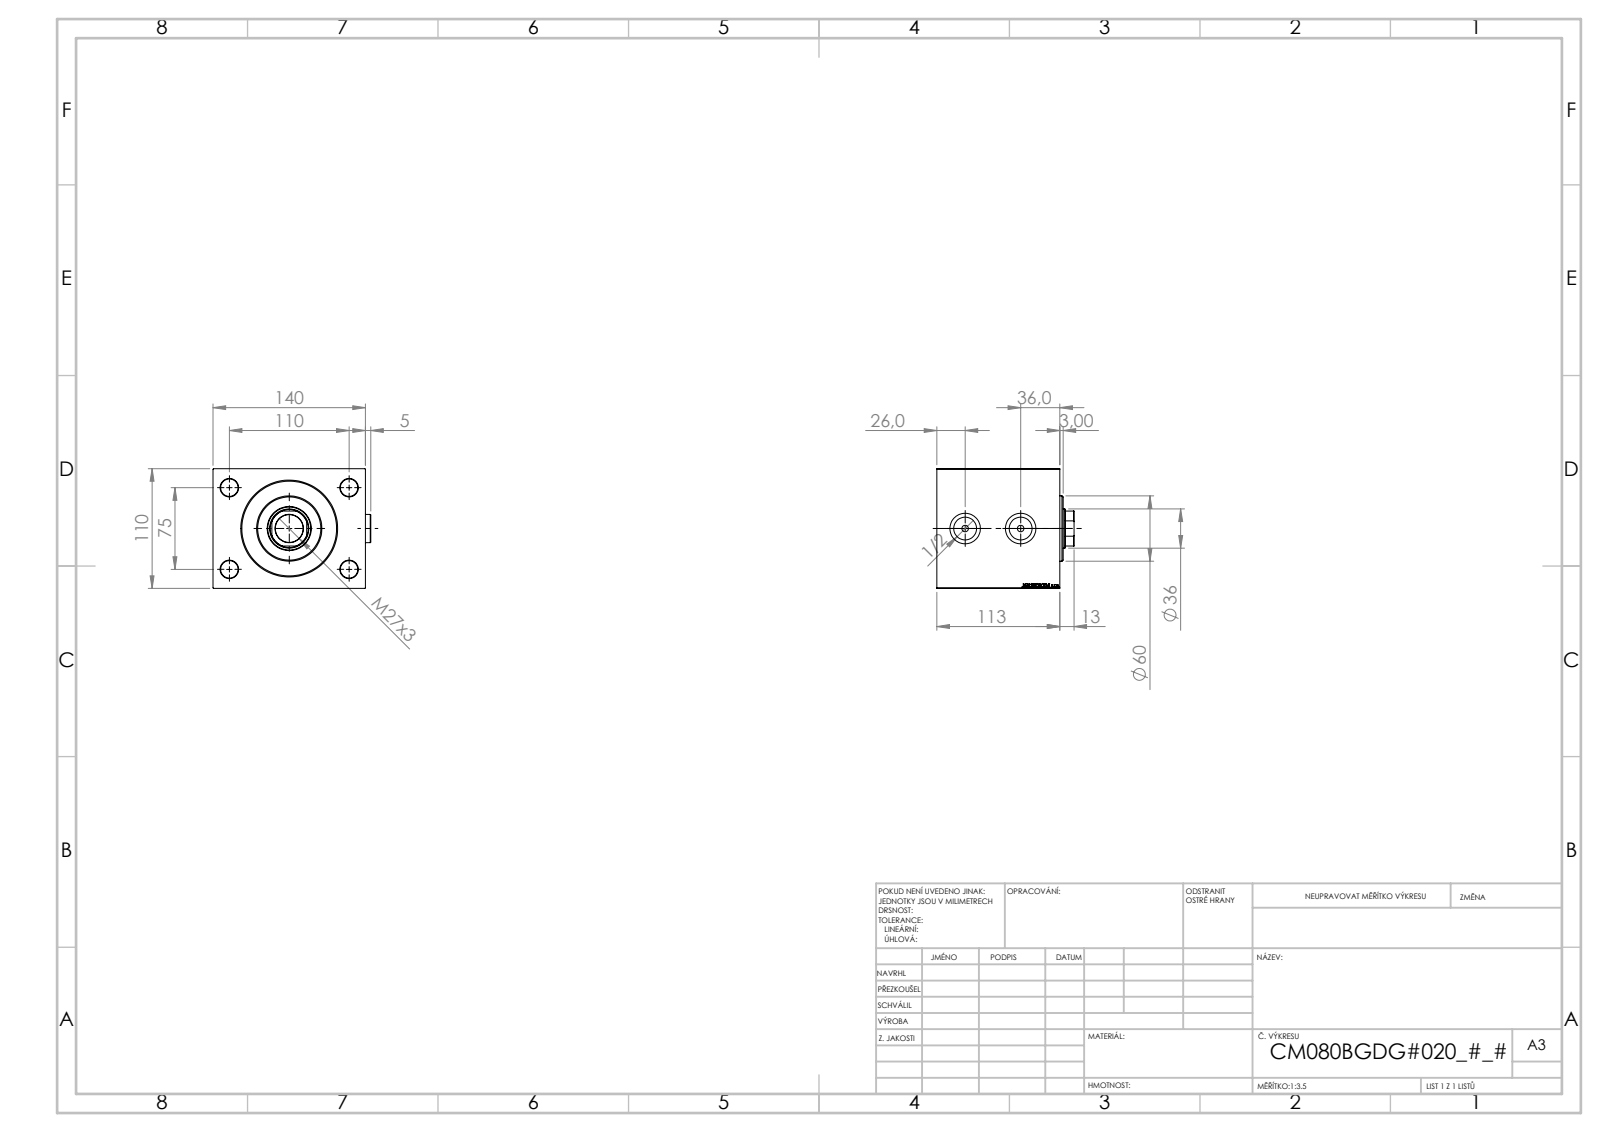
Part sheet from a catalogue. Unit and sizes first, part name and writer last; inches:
Units: inches
Overall size (bounding box): 5.705 × 4.961 × 4.331
Round holes (diameter × count): ⌀0.63 ×4, ⌀0.236 ×2, ⌀0.825 ×2, ⌀1.102 ×2, ⌀1.004 ×1, ⌀1.417 ×1, ⌀1.555 ×1, ⌀1.594 ×1, ⌀3.15 ×1, ⌀3.228 ×1, ⌀3.425 ×1
Round bosses / shafts (diameter × count): ⌀1.024 ×2, ⌀2.362 ×1
Partial cylindrical surfaces — rounded edges, fillets, slot ends (radius × count): R0.689 ×1
Main face-to-face distances: 4.331, 4.449, 5.512, 2.008, 2.441, 0.85, 1.157, 3.598, 0.394, 1.244
Hole centre spacings: 2.621, 2.953, 4.331, 5.242, 2.008
Volume: 99.53 in³ · Surface area: 252.4 in²
Bodies: 5 solids, 936 faces (436 planar, 70 cylindrical, 430 other)
Part name (STEP PRODUCT): V450CM_B_Body; Zatka_OIL_PORT; V450CM_B_VCP; V450CM_VC_B
STEP written by: SolidWorks 2019 (CONFIG_CONTROL_DESIGN)
